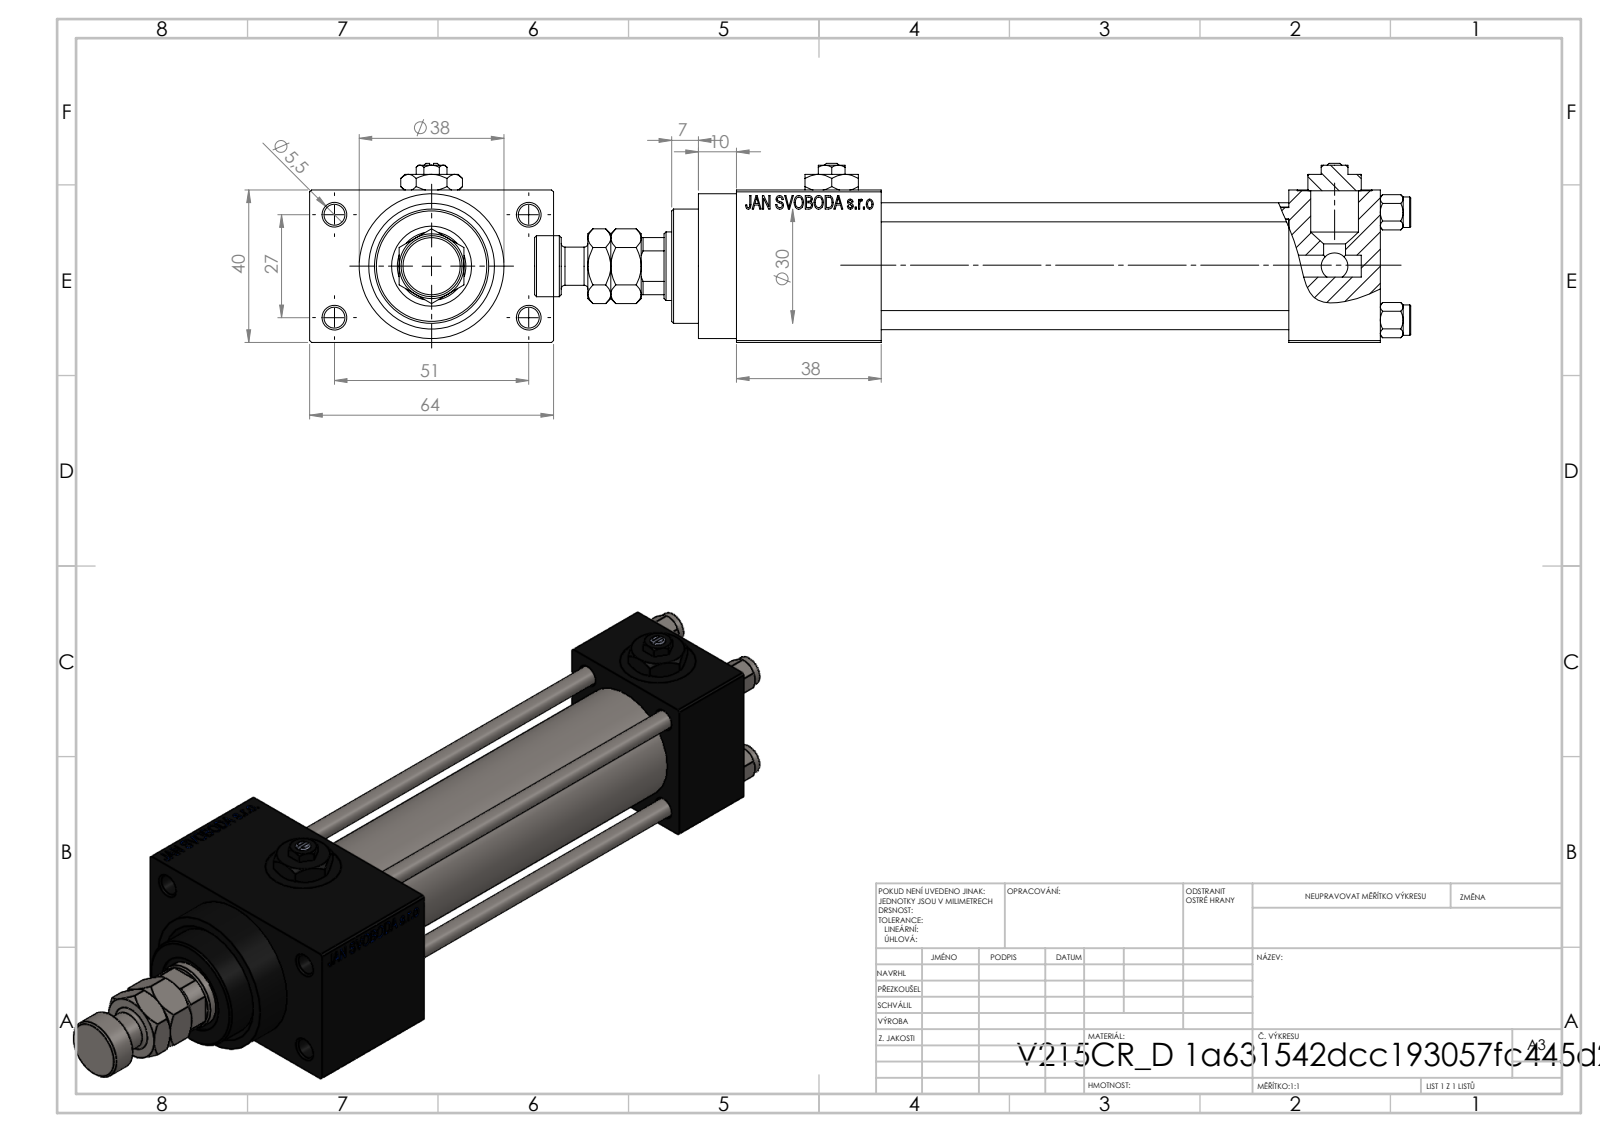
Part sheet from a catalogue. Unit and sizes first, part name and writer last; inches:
Units: inches
Overall size (bounding box): 9.055 × 2.52 × 1.85
Round holes (diameter × count): ⌀0.787 ×5, ⌀0.197 ×4, ⌀0.217 ×4, ⌀0.518 ×4, ⌀0.276 ×3, ⌀0.335 ×1, ⌀0.709 ×1, ⌀0.827 ×1, ⌀0.984 ×1, ⌀1.181 ×1
Round bosses / shafts (diameter × count): ⌀0.315 ×4, ⌀1.496 ×1, ⌀1.22 ×1, ⌀0.63 ×1, ⌀0.394 ×1
Partial cylindrical surfaces — rounded edges, fillets, slot ends (radius × count): R0.335 ×1
Main face-to-face distances: 1.575, 0.472, 4.213, 2.047, 0.945, 5.157, 1.496, 5.709, 6.654, 2.52
Hole centre spacings: 0.448, 0.788, 1.114, 1.136, 1.177, 1.561, 1.903, 1.063
Volume: 13.38 in³ · Surface area: 133.4 in²
Bodies: 14 solids, 1252 faces (557 planar, 101 cylindrical, 594 other)
Part name (STEP PRODUCT): MFA; NUT_M5_D; V215CR_D_Body; Zatka_pro_OIL_PORT (+3 more)
STEP written by: SolidWorks 2019 (CONFIG_CONTROL_DESIGN)
